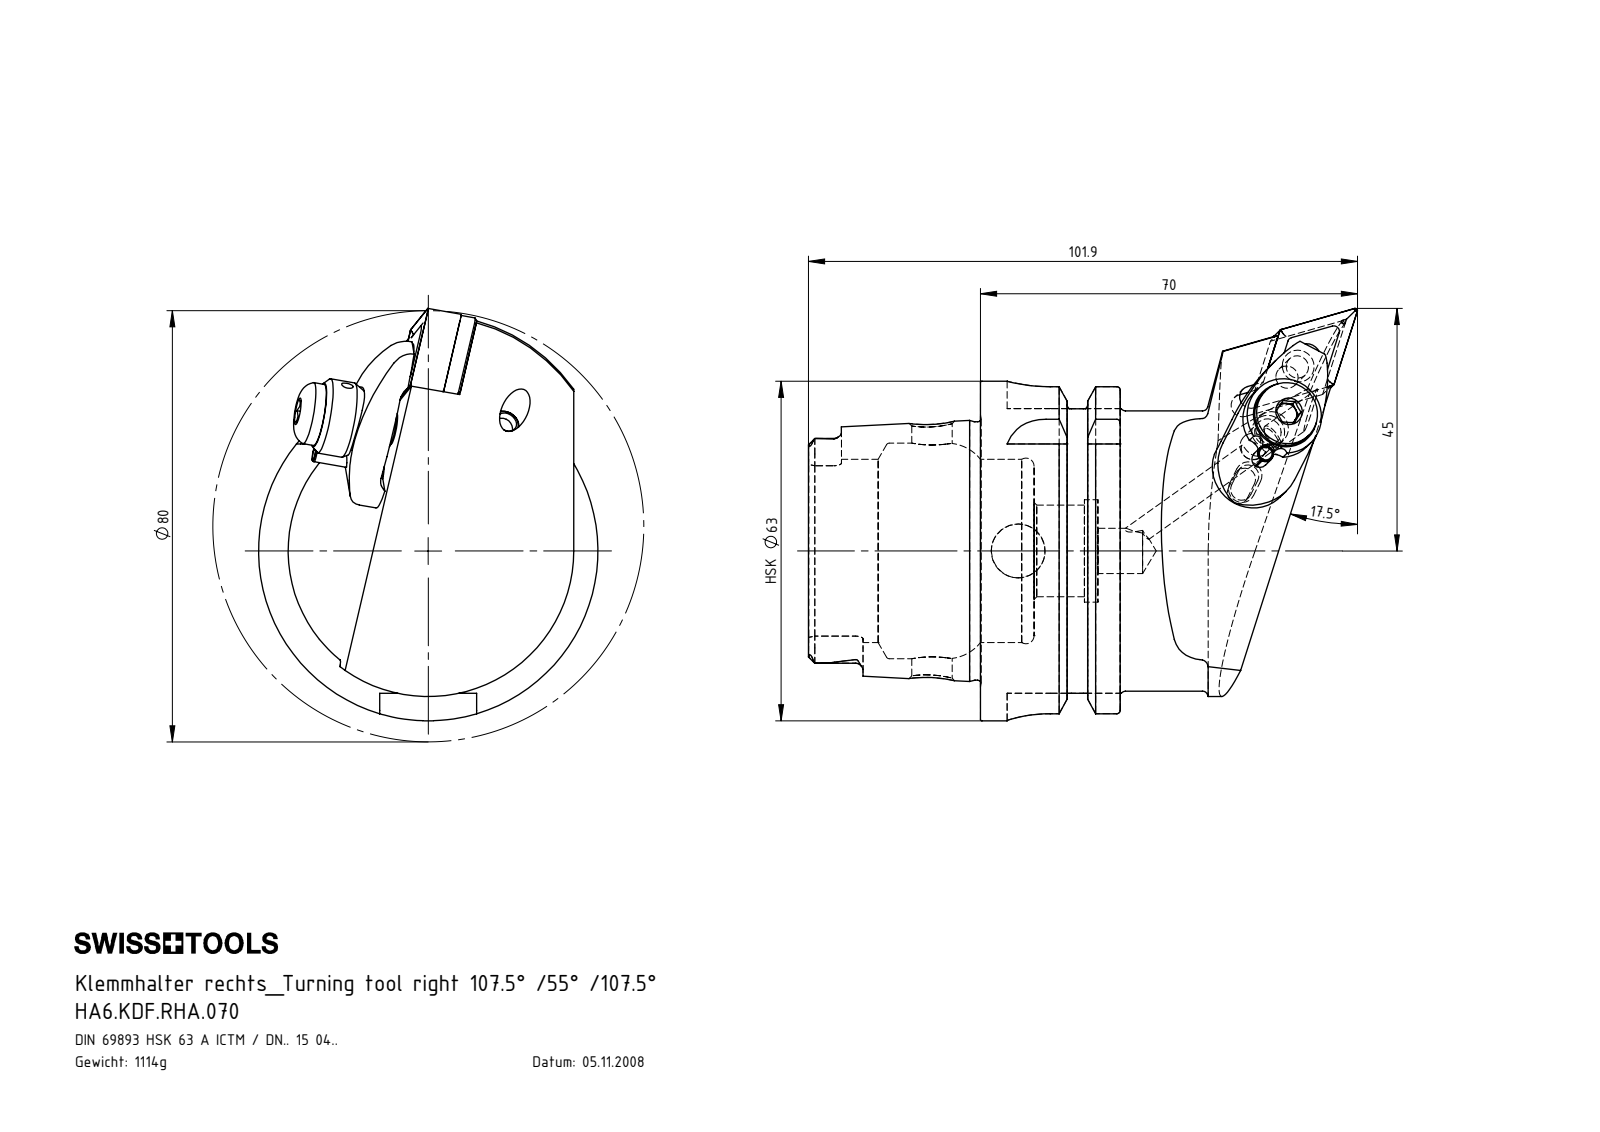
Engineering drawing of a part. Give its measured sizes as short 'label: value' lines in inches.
name: DNMG150604; WCC-ER5.102.005_A; HA6-KDF.RHA.070_C; WCC-ER4.103.032_A (+7 more)
written by: SolidWorks 2017 (AUTOMOTIVE_DESIGN)
unit: in
bodies: 11 solids, 463 faces (123 planar, 152 cylindrical, 188 other)
size: 4.012 × 3.012 × 2.48
volume: 8.718 in³; area: 53.89 in²
holes: 3× ⌀0.079, 2× ⌀0.165, 2× ⌀0.276, 1× ⌀0.094, 1× ⌀0.118, 1× ⌀0.157, 1× ⌀0.197, 1× ⌀0.203, 1× ⌀0.244, 1× ⌀0.256, 1× ⌀0.295, 1× ⌀0.331
bosses: 2× ⌀0.197, 2× ⌀0.118, 1× ⌀2.48, 1× ⌀2.163, 1× ⌀2.047, 1× ⌀1.887, 1× ⌀0.551, 1× ⌀0.453
rounds: 6× R0.015, 6× R0.027, 6× R0.055, 4× R0.016, 4× R0.315, 3× R0.059, 2× R0.079, 2× R0.111
face distances: 1.022, 0.63, 0.392, 1.256, 1.648, 2.278, 0.238, 2.079, 0.858, 0.125
hole spacings: 0.591, 0.906, 0.315, 0.583, 0.323, 0.315, 0.591, 0.905
